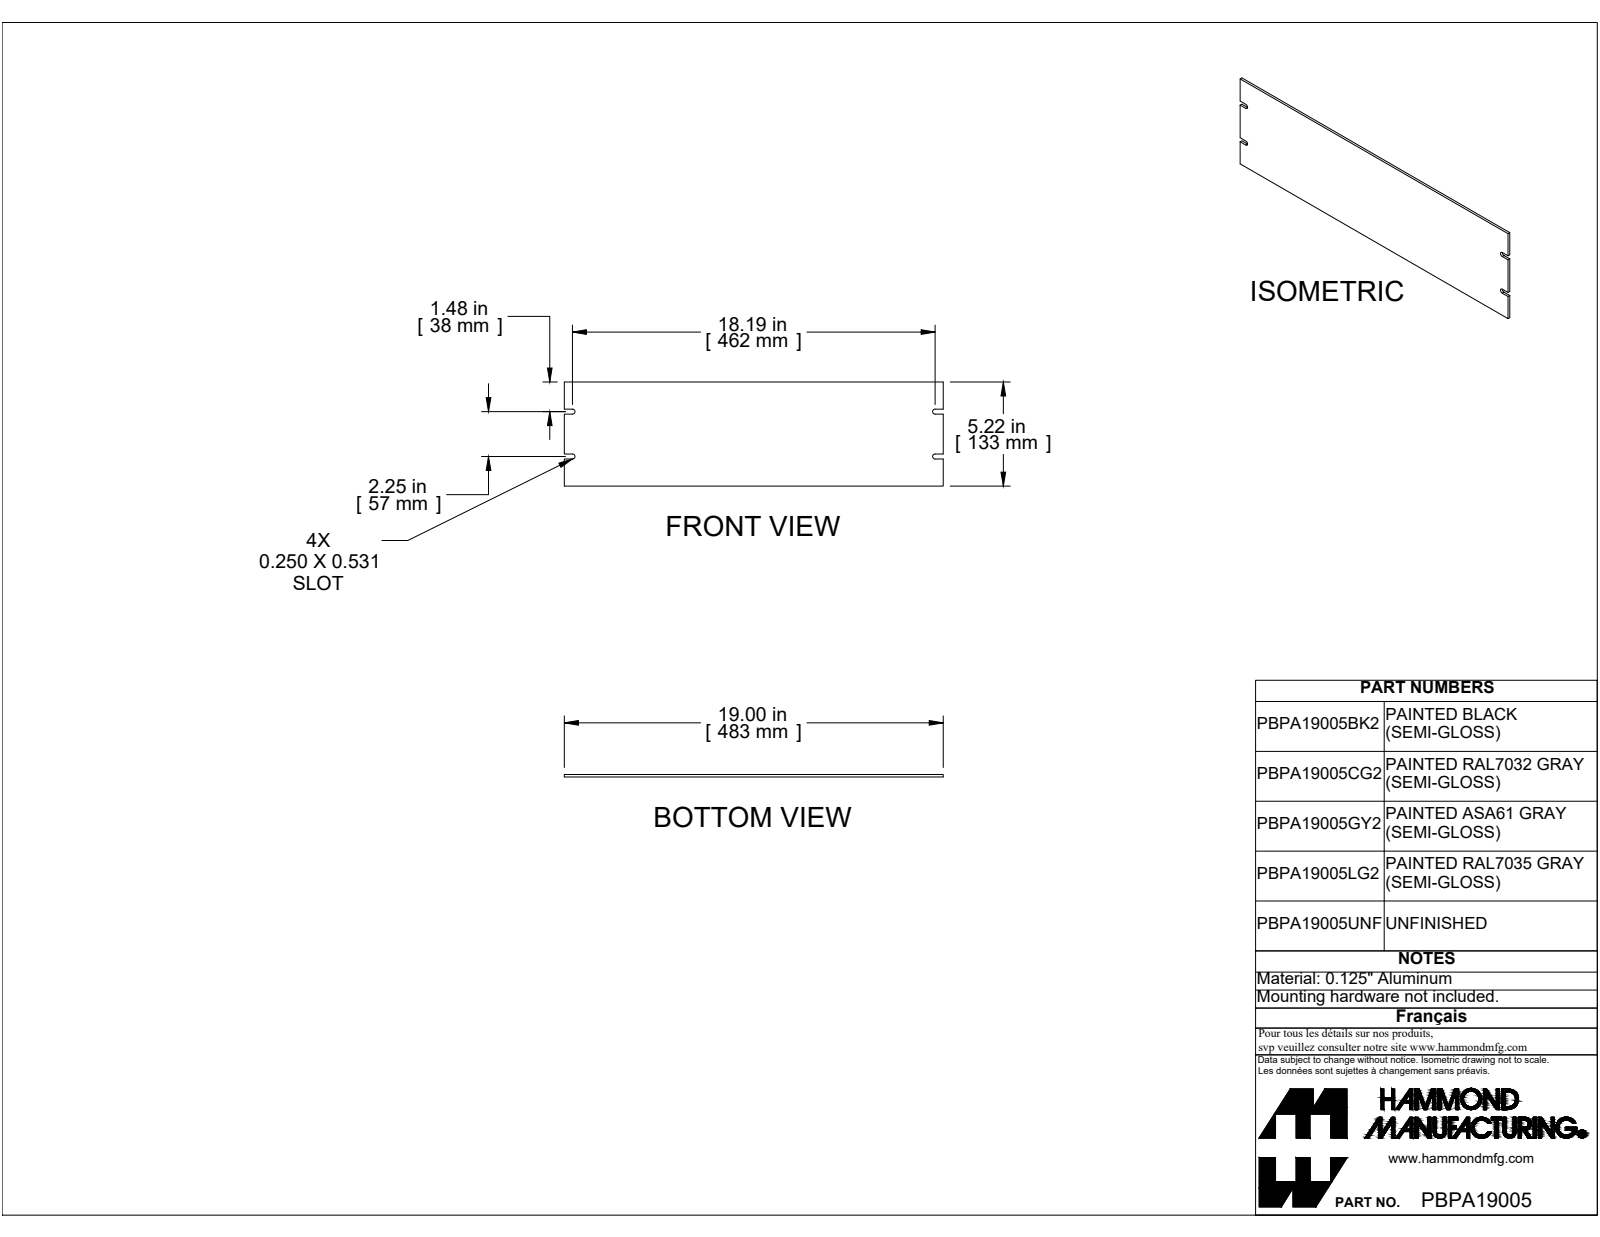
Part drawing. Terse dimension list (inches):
name: PBPA19005UNF
written by: SolidWorks 2019 (CONFIG_CONTROL_DESIGN)
unit: in
bodies: 1 solid, 22 faces (18 planar, 4 cylindrical, 0 other)
size: 19 × 5.218 × 0.125
volume: 12.33 in³; area: 203.8 in²
rounds: 4× R0.125
face distances: 0.125, 5.218, 19, 1.359, 1.609, 3.609, 3.859, 2.25, 0.25, 2.5
